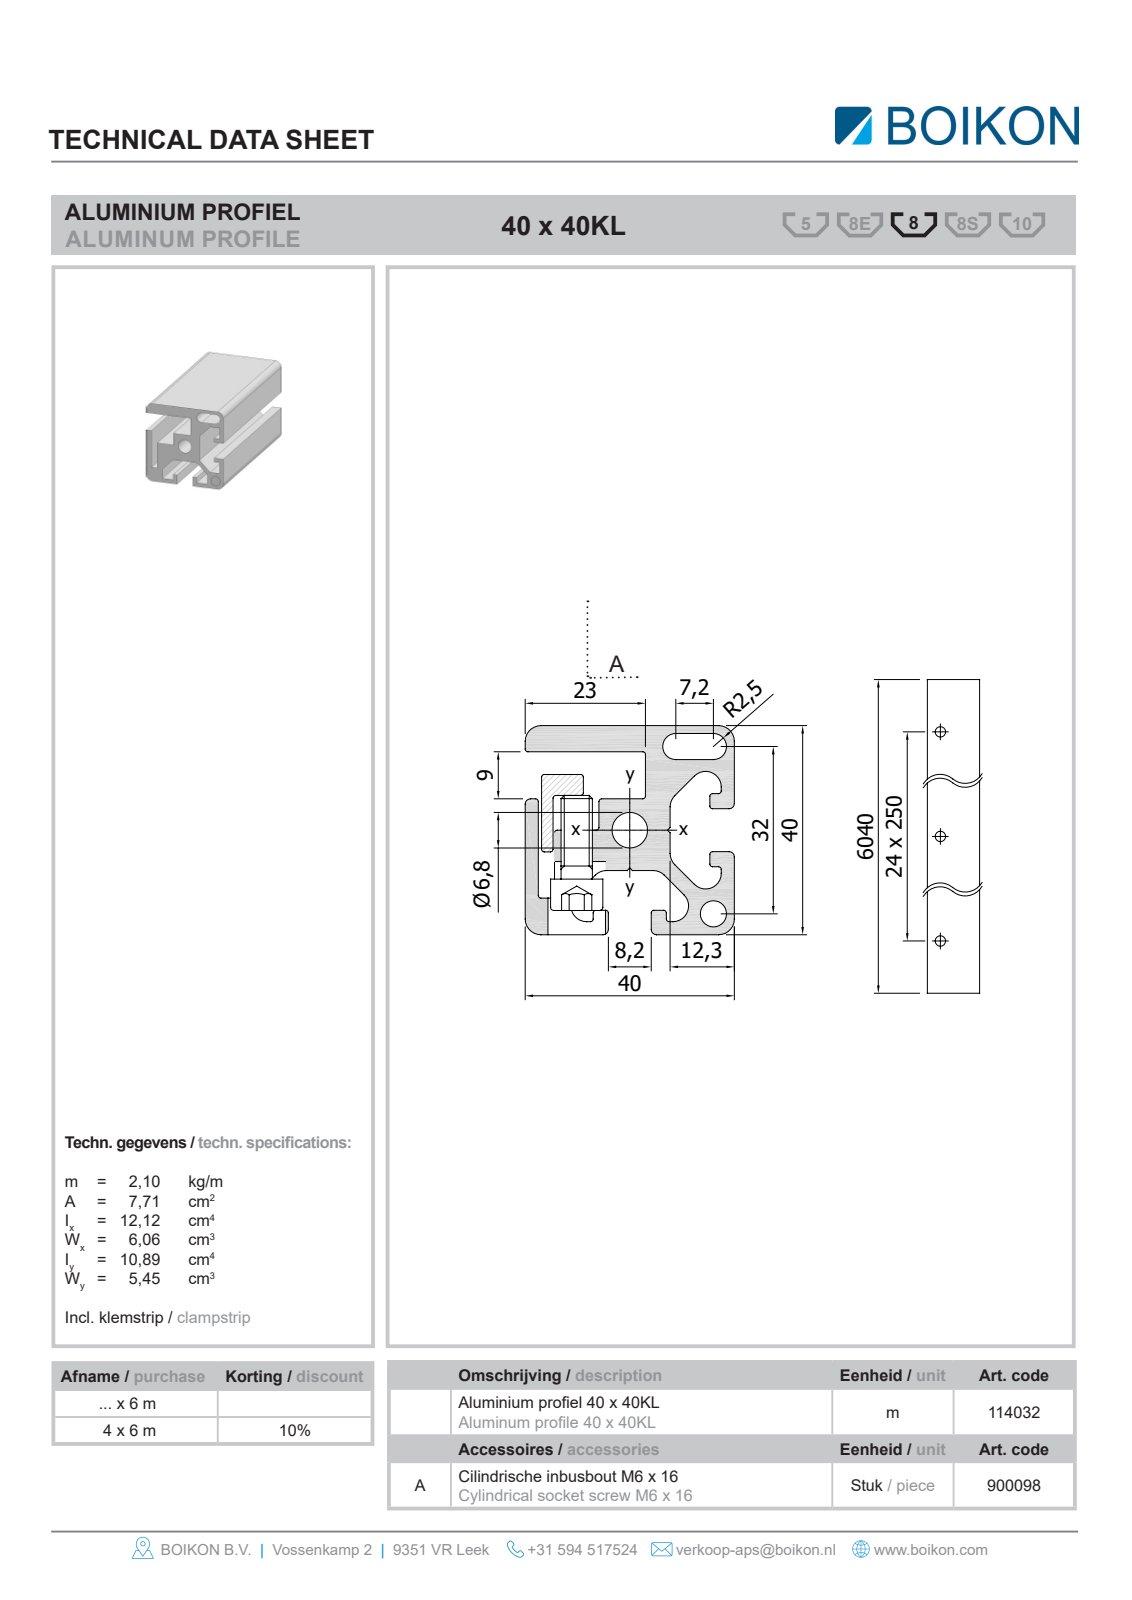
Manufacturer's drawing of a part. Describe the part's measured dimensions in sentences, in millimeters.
The part is named "Root; 11403240x40-KLBOIKON0". Its 3-D file was written by "HiCAD 2013 1802.4 Build 509 (AUTOMOTIVE_DESIGN)". It is 2 solids with 56 faces: 48 planar, 8 cylindrical and 0 other. Overall it measures 1000 by 40 by 40 millimeters. Its volume is 766 878 cubic millimeters and its surface area 426 924 square millimeters. Round holes: 1 of diameter 6.8. Round bosses or shafts: 1 of diameter 5. Partial cylindrical surfaces (rounded edges, fillets, slot ends): 4 of radius 3, 2 of radius 2.5. The main face-to-face distances are 40, 2, 5, 12.4, 10.4, 27.6, 24.1, 35, 38, 22.1.
